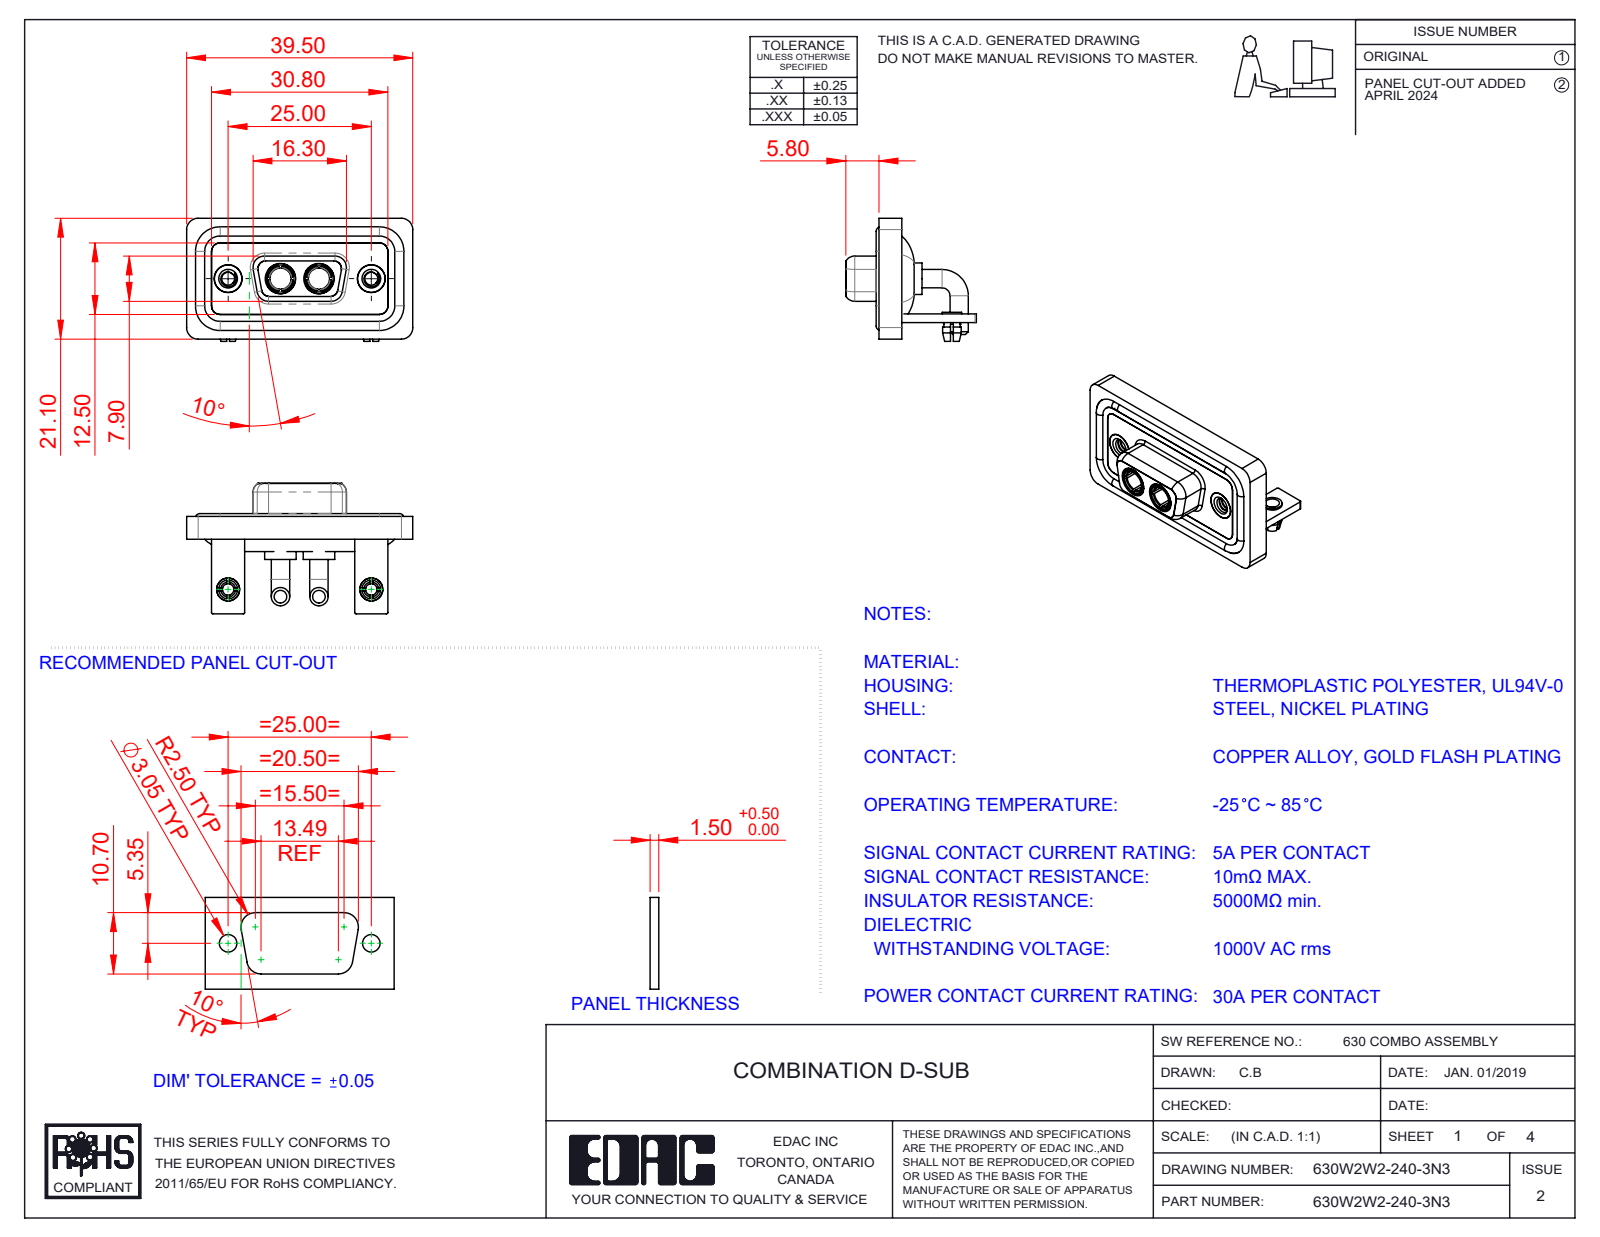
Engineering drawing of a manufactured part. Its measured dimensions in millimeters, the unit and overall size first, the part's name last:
Units: millimetres
Overall size (bounding box): 39.5 × 22.8 × 21.5
Round holes (diameter × count): ⌀4.85 ×4, ⌀2 ×2, ⌀2.26 ×2, ⌀2.5 ×2, ⌀3.2 ×2, ⌀3.7 ×2, ⌀4 ×2, ⌀4.05 ×2, ⌀5 ×2, ⌀5.3 ×2
Round bosses / shafts (diameter × count): ⌀3.2 ×4, ⌀1.6 ×4, ⌀5.5 ×2, ⌀5.2 ×2, ⌀4.96 ×2, ⌀4.95 ×2, ⌀4.8 ×2, ⌀4.75 ×2
Partial cylindrical surfaces — rounded edges, fillets, slot ends (radius × count): R2 ×19, R1.5 ×18, R0.25 ×16, R1.35 ×8, R1.6 ×8, R0.5 ×5, R0.6 ×4, R0.65 ×4
Main face-to-face distances: 0.4, 2.9, 1.5, 1.8, 1.1, 3.7, 0.8, 2.5, 1.6, 3.1
Hole centre spacings: 9.14, 15.86, 25, 6.72
Volume: 5 275 mm³ · Surface area: 8 768 mm²
Bodies: 15 solids, 682 faces (231 planar, 294 cylindrical, 157 other)
Part name (STEP PRODUCT): 630Combo Stabilizer Bracket_50 Contacts; 630Combo Board Lock_50 Contacts; 630Combo Housing_2W2; 630Combo Shell Front_09 Contacts (+5 more)
STEP written by: SolidWorks 2023 (CONFIG_CONTROL_DESIGN)
